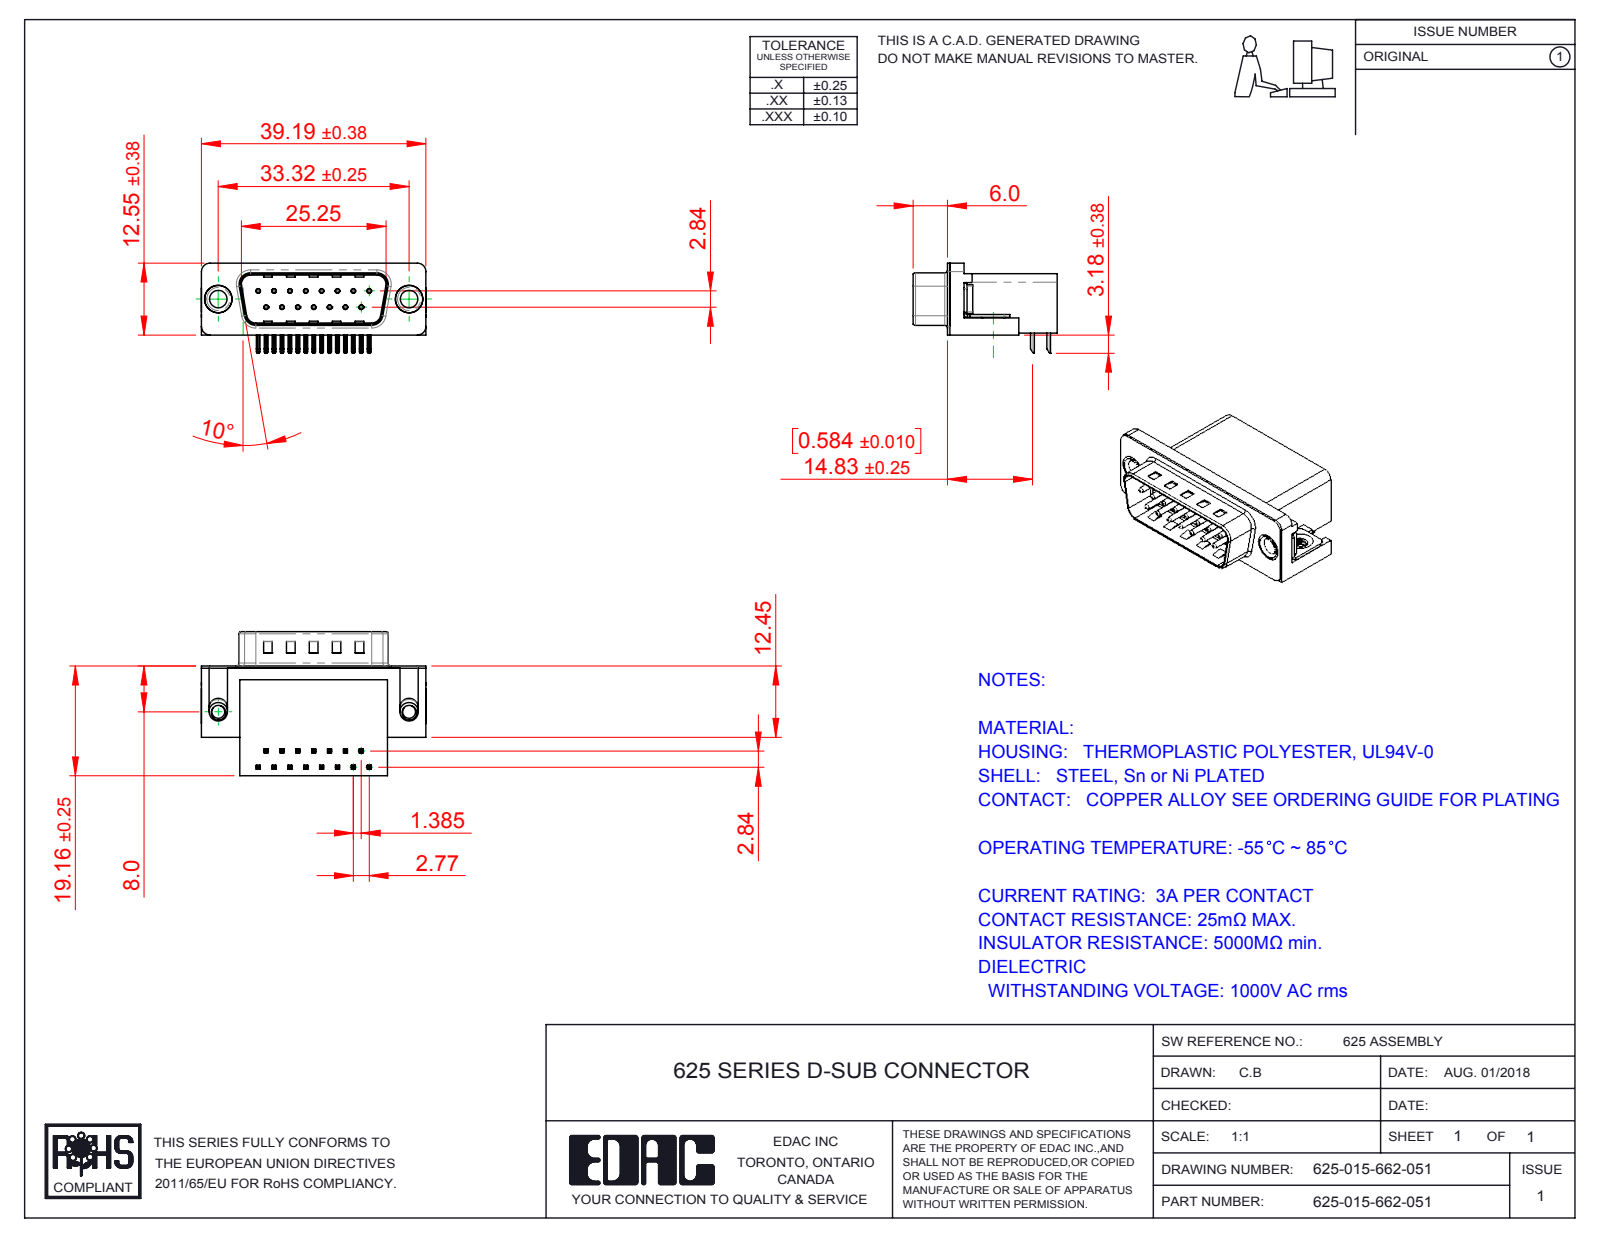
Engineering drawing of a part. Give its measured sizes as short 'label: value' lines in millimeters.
name: 625-015-662-051; 625 4-40 Threaded Board Mount; 625 Housing_15 Socket; 625 Contact Bottom (+3 more)
written by: SolidWorks 2016 (CONFIG_CONTROL_DESIGN)
unit: mm
bodies: 21 solids, 1471 faces (895 planar, 441 cylindrical, 135 other)
size: 39.22 × 25.16 × 15.73
volume: 6 242 mm³; area: 6 480 mm²
holes: 15× ⌀0.35, 15× ⌀0.8, 2× ⌀2.26, 2× ⌀3.05, 2× ⌀4, 2× ⌀4.8, 2× ⌀5
bosses: 15× ⌀0.75, 2× ⌀4.9, 2× ⌀4.75, 2× ⌀3.85, 2× ⌀3.26
rounds: 68× R0.25, 30× R0.12, 16× R1, 9× R0.5, 8× R1.6, 6× R1.5, 4× R0.9, 4× R2
face distances: 0.4, 10.35, 18.76, 2.1, 19.16, 10.46, 1.7, 10.86, 8.76, 16.26
hole spacings: 3.16, 2.77, 5.54, 8.31, 11.08, 5.03, 5.04, 7.48
